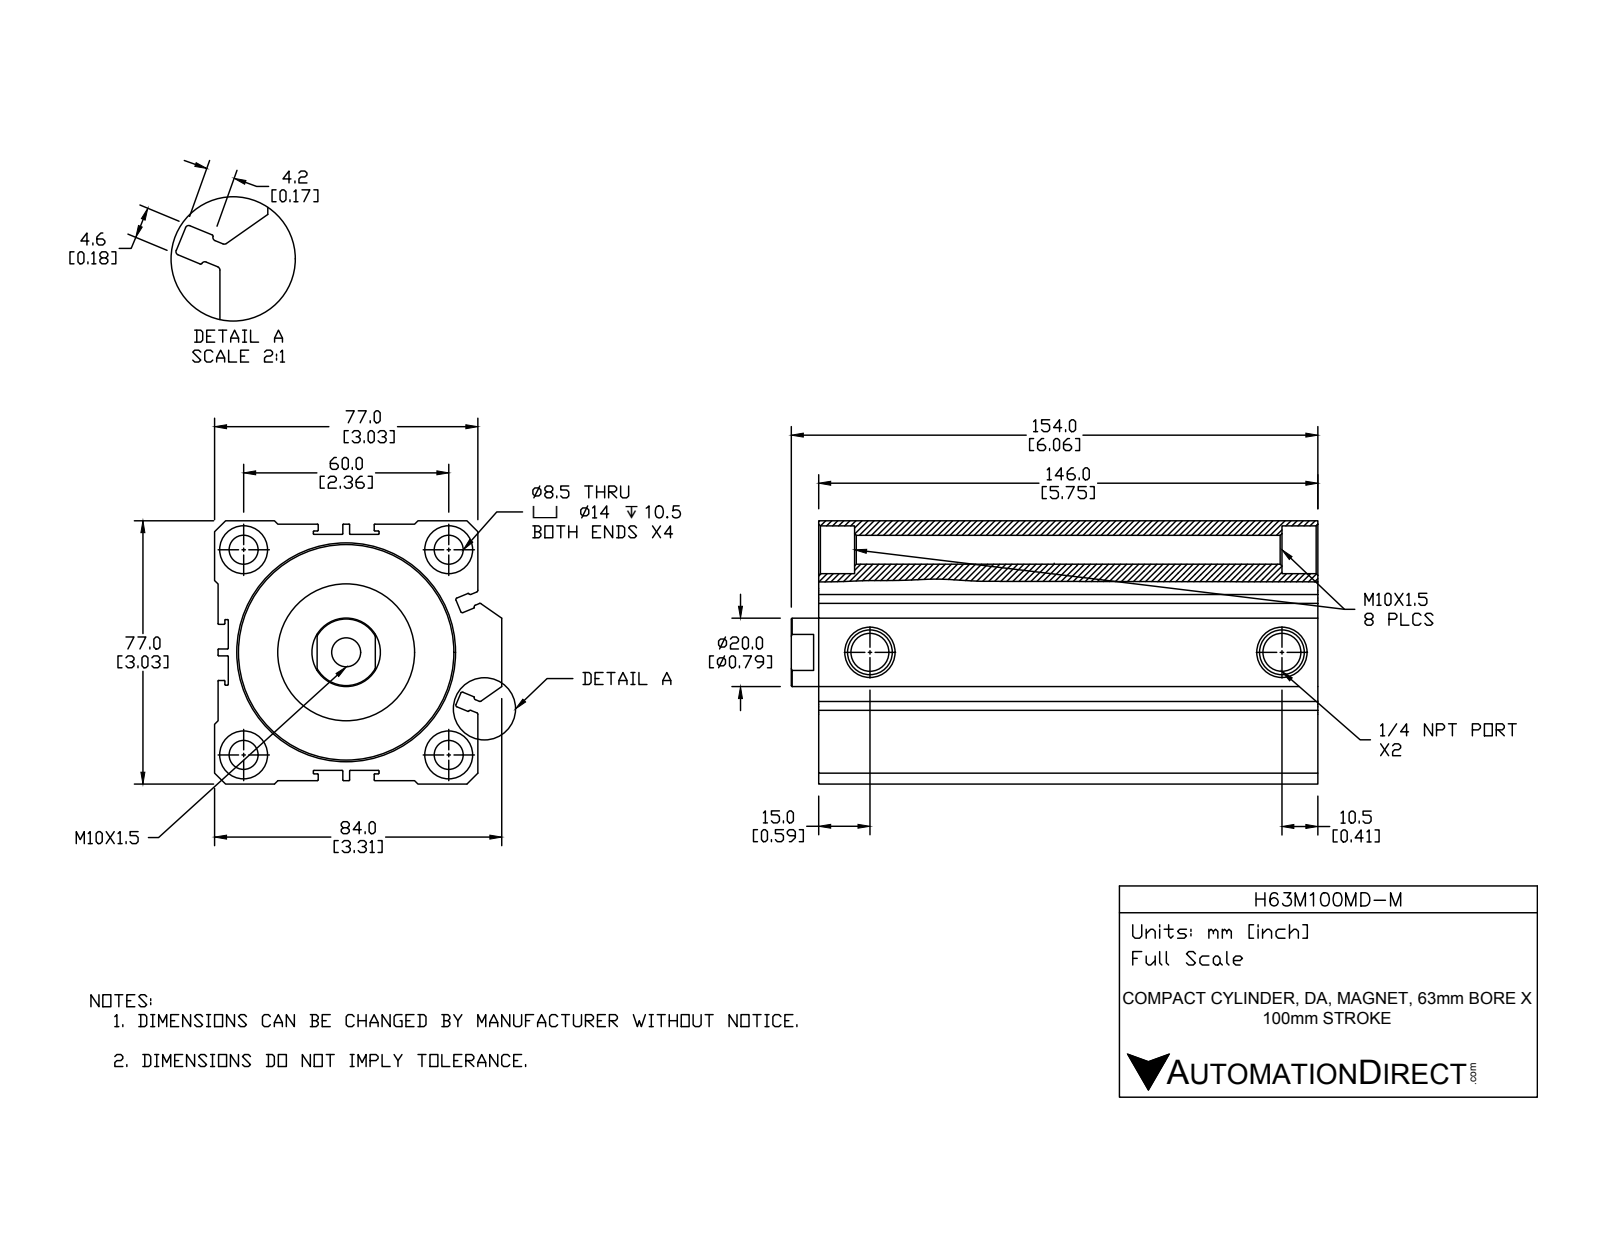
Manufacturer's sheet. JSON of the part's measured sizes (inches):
{"part_name": "H63M100MD-M; H63M100MD-M-BODY; H63M100MD-M-PISTON", "step_written_by": "SolidWorks 2015 (CONFIG_CONTROL_DESIGN)", "units": "inches", "bodies": {"solids": 2, "faces": 255, "planar": 99, "cylindrical": 103, "other": 53}, "overall_size": [6.063, 3.307, 3.031], "volume_in3": 30.53, "surface_area_in2": 213.4, "round_holes": [[0.335, 5], [0.551, 4], [0.438, 2], [0.787, 1], [1.792, 1], [2.48, 1]], "round_bosses_or_shafts": [[1.575, 1], [1.535, 1]], "partial_cylinders_radius": [[0.008, 40], [0.02, 12]], "face_to_face_distances": [0.039, 2.992, 0.118, 3.031, 0.157, 2.874, 2.835, 0.079, 2.953, 0.906], "hole_center_spacings": [1.67, 2.362, 3.341, 4.744]}
